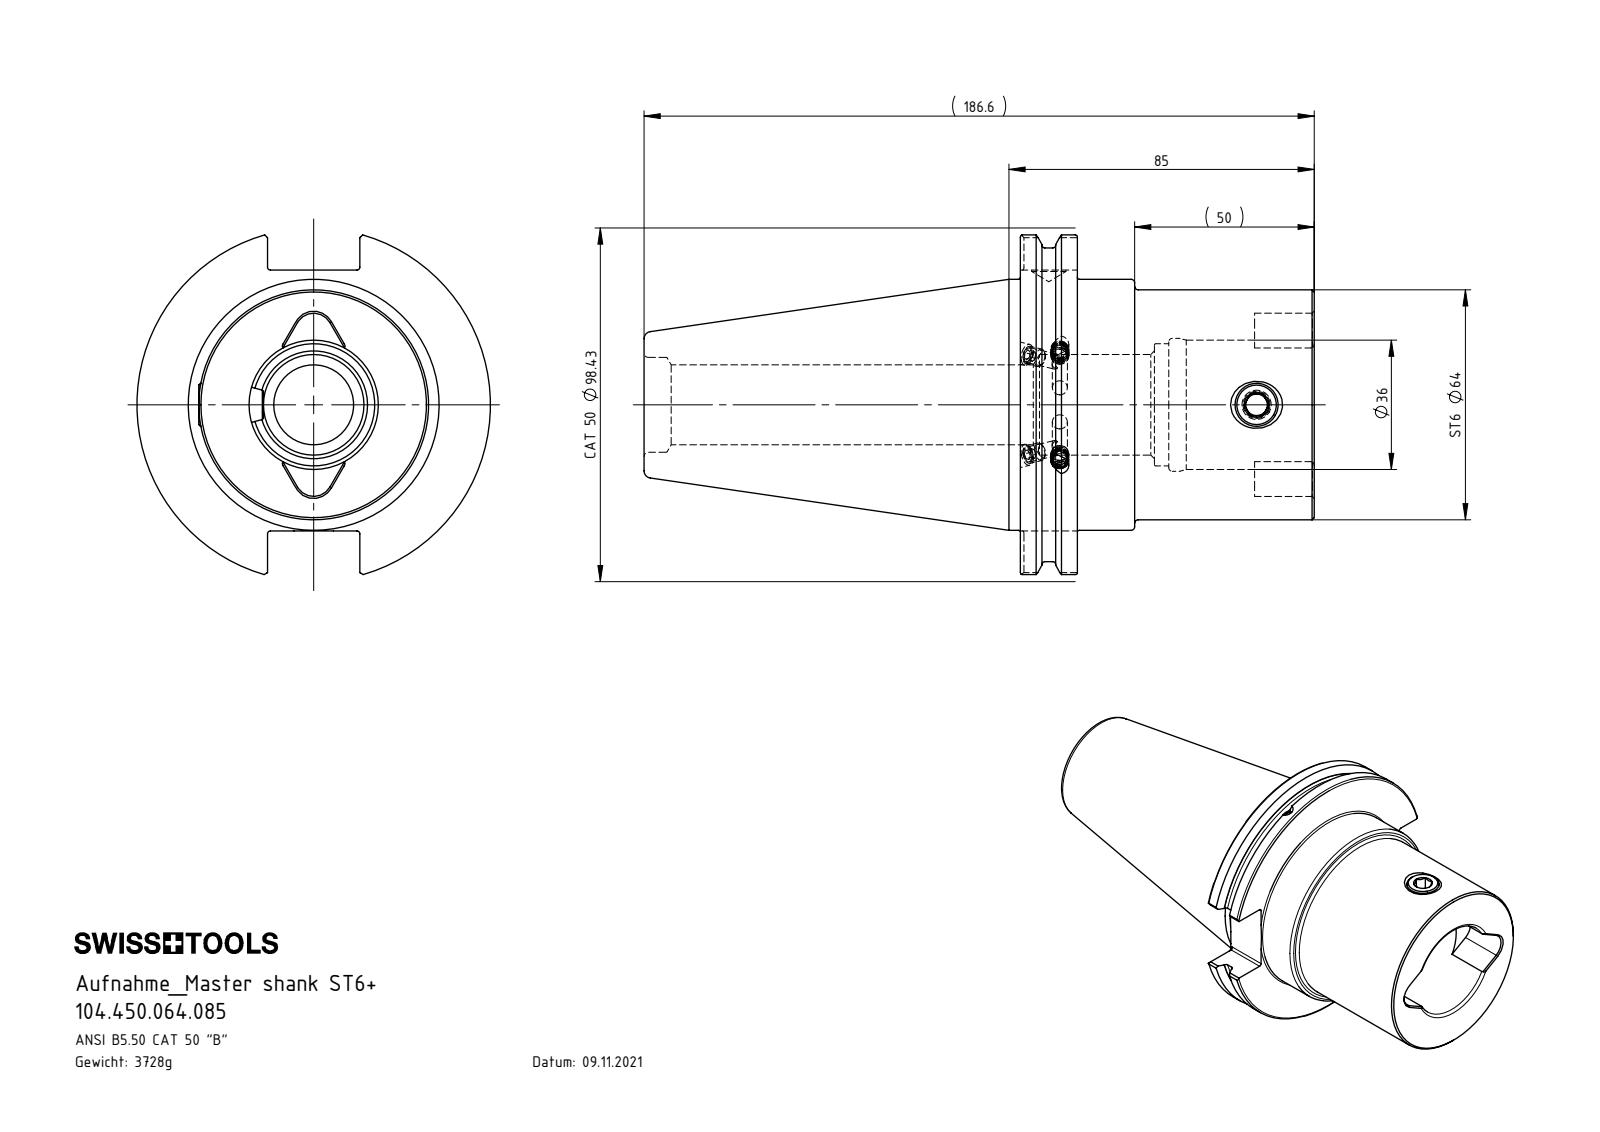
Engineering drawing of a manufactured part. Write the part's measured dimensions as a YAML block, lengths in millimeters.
part_name: "CB5-ST6.K01.085_C; KVT_MB_600_050; ST6-ER1.001.018_A; 104.450.064.085 (+1 more)"
step_written_by: "SolidWorks 2022 (CONFIG_CONTROL_DESIGN)"
units: millimeters
bodies: {solids: 8, faces: 285, planar: 75, cylindrical: 75, other: 135}
overall_size: [186.6, 98.42, 94.52]
volume: 474847
surface_area: 67159
round_holes:
  - {diameter: 4.2, count: 3}
  - {diameter: 6, count: 3}
  - {diameter: 4, count: 2}
  - {diameter: 5, count: 1}
  - {diameter: 9.5, count: 1}
  - {diameter: 11, count: 1}
  - {diameter: 22.25, count: 1}
  - {diameter: 26.4, count: 1}
  - {diameter: 28, count: 1}
  - {diameter: 34, count: 1}
  - {diameter: 36, count: 1}
  - {diameter: 37, count: 1}
round_bosses_or_shafts:
  - {diameter: 5, count: 4}
  - {diameter: 98.42, count: 1}
  - {diameter: 91, count: 1}
  - {diameter: 69.85, count: 1}
  - {diameter: 64, count: 1}
  - {diameter: 12, count: 1}
partial_cylinders:
  - {radius: 0.8, count: 8}
  - {radius: 5.2, count: 2}
face_to_face_distances: [15.87, 81.82, 65.95, 104.78, 120.65, 186.6, 72.6, 30.7, 25.7, 136.6]
